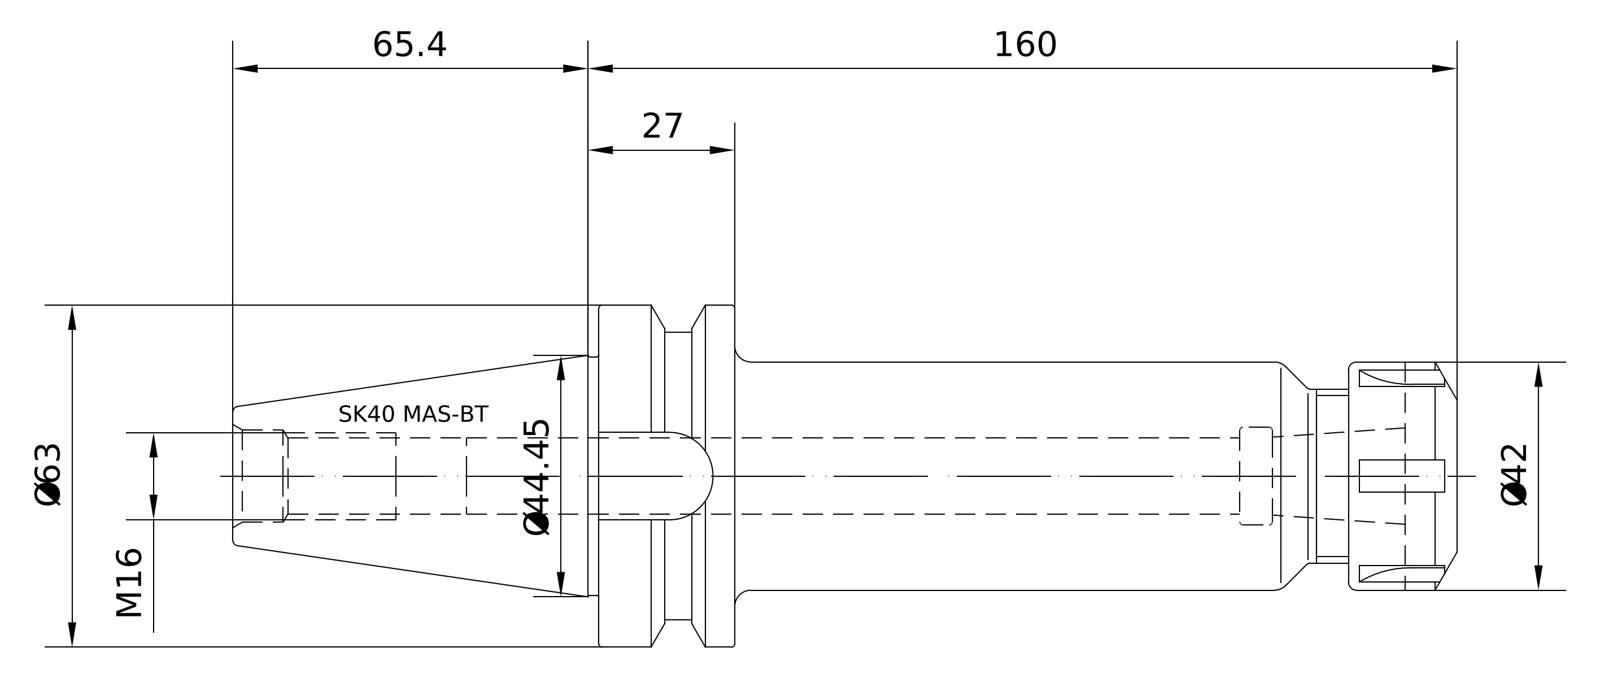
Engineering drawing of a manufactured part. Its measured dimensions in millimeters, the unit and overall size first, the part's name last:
Units: millimetres
Overall size (bounding box): 225.4 × 62.98 × 62.98
Round holes (diameter × count): ⌀13.84 ×1, ⌀17.01 ×1, ⌀17.5 ×1, ⌀18 ×1
Round bosses / shafts (diameter × count): ⌀62.98 ×1, ⌀52.75 ×1, ⌀43.75 ×1, ⌀42 ×1, ⌀32 ×1, ⌀16.01 ×1
Partial cylindrical surfaces — rounded edges, fillets, slot ends (radius × count): R8.1 ×1
Main face-to-face distances: 113, 25, 138, 158, 133, 20, 44.9, 146, 121, 8
Volume: 294 926 mm³ · Surface area: 44 457 mm²
Bodies: 2 solids, 146 faces (46 planar, 26 cylindrical, 74 other)
Part name (STEP PRODUCT): 40-522-25; 83-912-25; 40-522-25_ASM
STEP written by: PRO/ENGINEER BY PARAMETRIC TECHNOLOGY CORPORATION, 2010430 (CONFIG_CONTROL_DESIGN)
